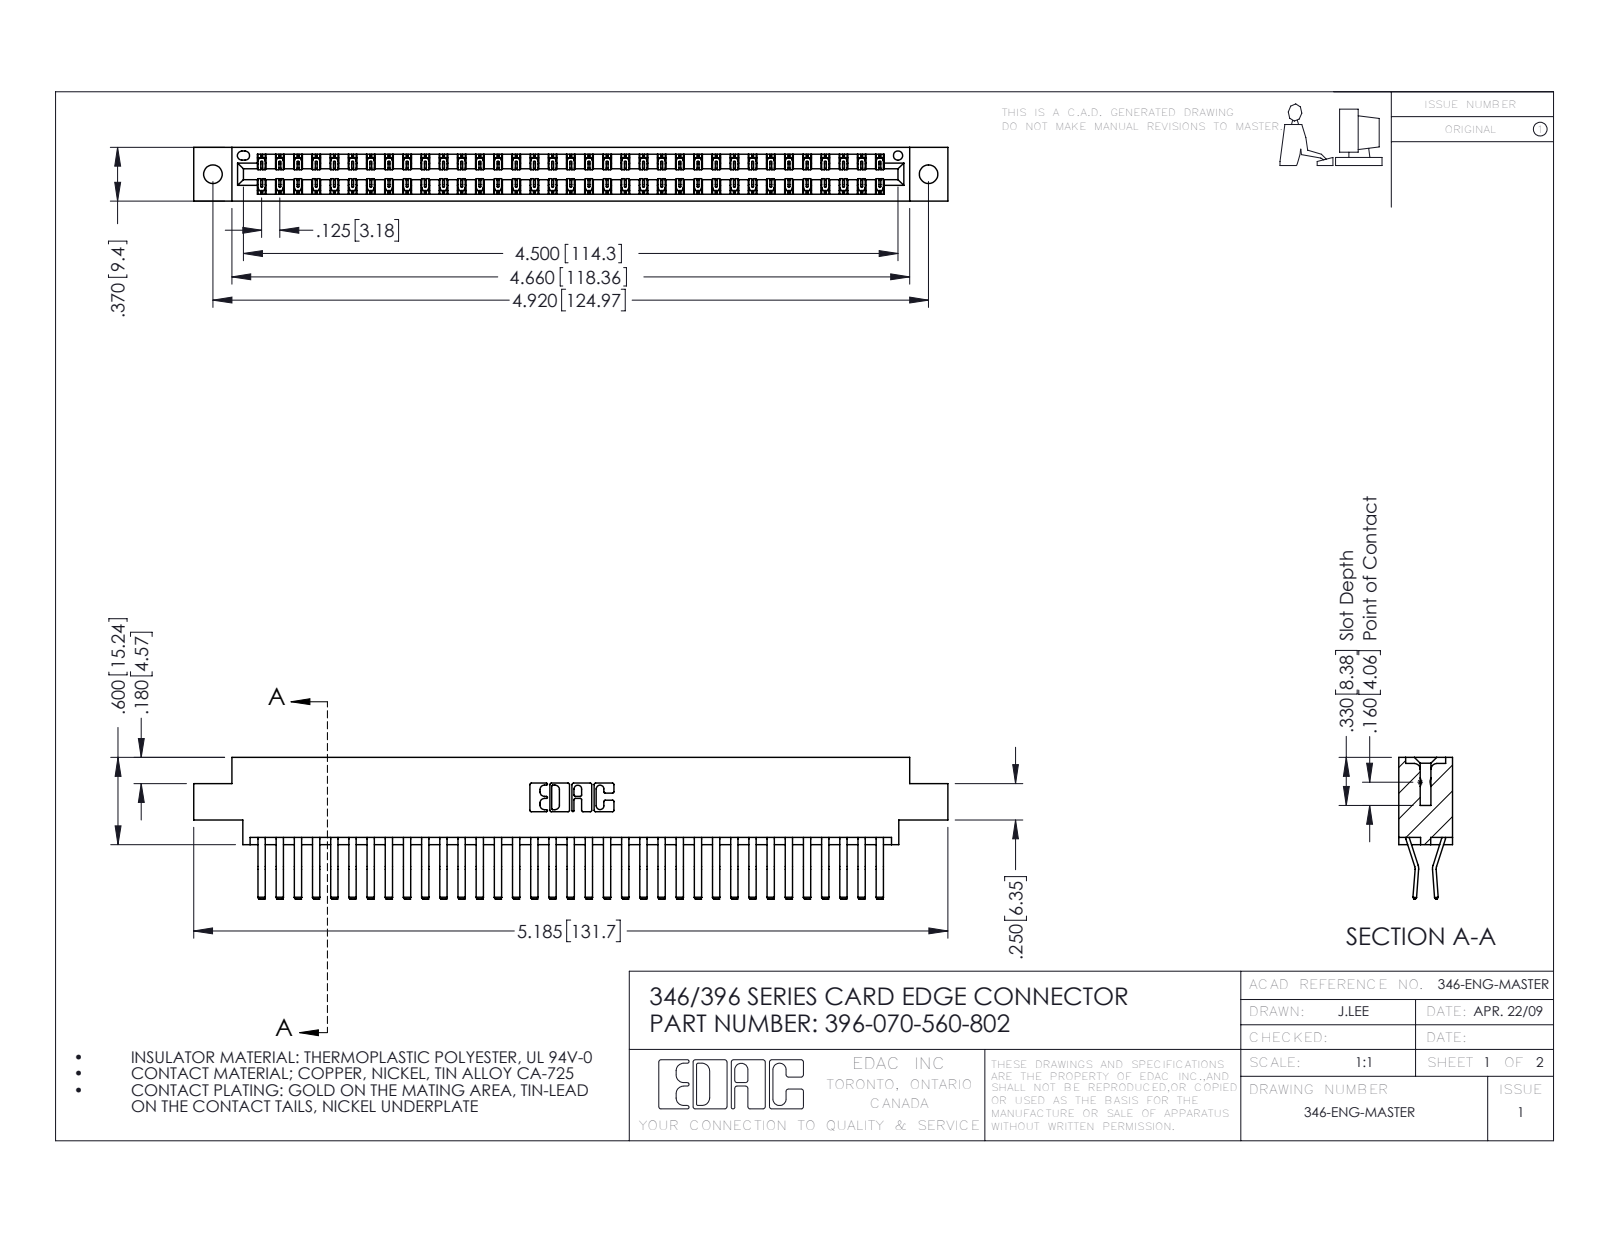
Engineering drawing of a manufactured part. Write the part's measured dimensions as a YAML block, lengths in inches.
part_name: "345-292-001_560 Tail; 396-070-560-802; 346 Part_0.170 Offset - 0.128 Dia"
step_written_by: "SolidWorks 2016 (CONFIG_CONTROL_DESIGN)"
units: inches
bodies: {solids: 71, faces: 3906, planar: 2530, cylindrical: 1376, other: 0}
overall_size: [5.185, 0.975, 0.37]
volume: 0.797
surface_area: 29.4
round_holes:
  - {diameter: 0.128, count: 2}
  - {diameter: 0.064, count: 1}
partial_cylinders:
  - {radius: 0.006, count: 105}
  - {radius: 0.01, count: 22}
  - {radius: 0.007, count: 6}
  - {radius: 0.031, count: 6}
  - {radius: 0.026, count: 3}
  - {radius: 0.01, count: 2}
  - {radius: 0.014, count: 2}
  - {radius: 0.022, count: 2}
face_to_face_distances: [0.048, 0.322, 0.37, 0.025, 0.25, 0.072, 0.298, 0.275, 0.148, 0.222]
hole_center_spacings: [0.246, 4.711, 4.92]
